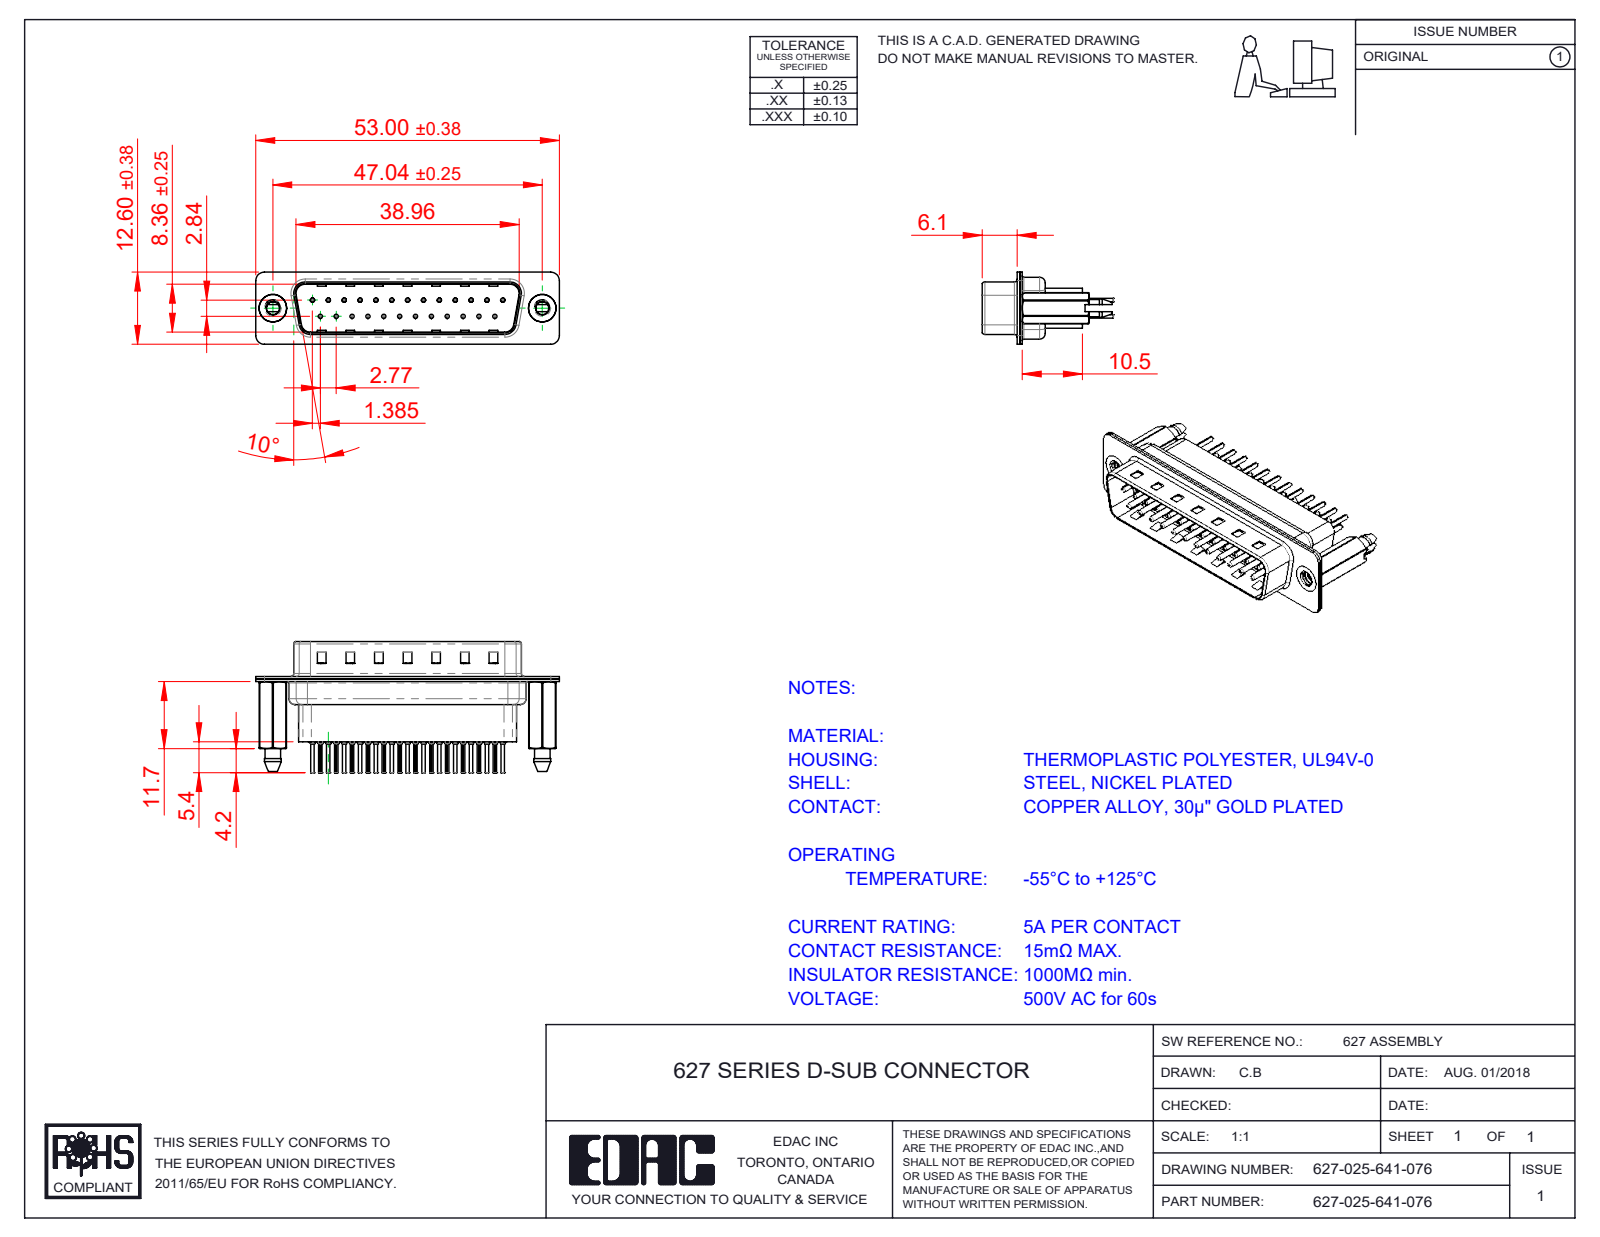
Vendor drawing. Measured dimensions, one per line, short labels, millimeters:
name: 627 Housing_25 HP; 627 Contact Row 2_41; 627 4-40 Threaded Boardlock_HP41; 627 Shell Front_25 Contacts (+3 more)
written by: SolidWorks 2020 (CONFIG_CONTROL_DESIGN)
unit: mm
bodies: 30 solids, 2934 faces (803 planar, 1128 cylindrical, 1003 other)
size: 53 × 22.8 × 12.6
volume: 4 090 mm³; area: 10 547 mm²
holes: 25× ⌀0.2, 25× ⌀0.35, 25× ⌀1.1, 25× ⌀1.6, 2× ⌀2.26, 2× ⌀4, 2× ⌀4.8
bosses: 25× ⌀2, 25× ⌀1.5, 25× ⌀0.75, 25× ⌀0.6, 2× ⌀4.9
rounds: 50× R0.1, 18× R1.5, 12× R2, 10× R1.6, 8× R0.5, 4× R0.25, 4× R0.6, 4× R0.65
face distances: 0.4, 0.45, 0.82, 9.58, 0.68, 7.68, 1.5, 0.9, 1.08, 8.08
hole spacings: 3.16, 8.31, 2.77, 5.54, 11.08, 16.62, 5.03, 5.04
